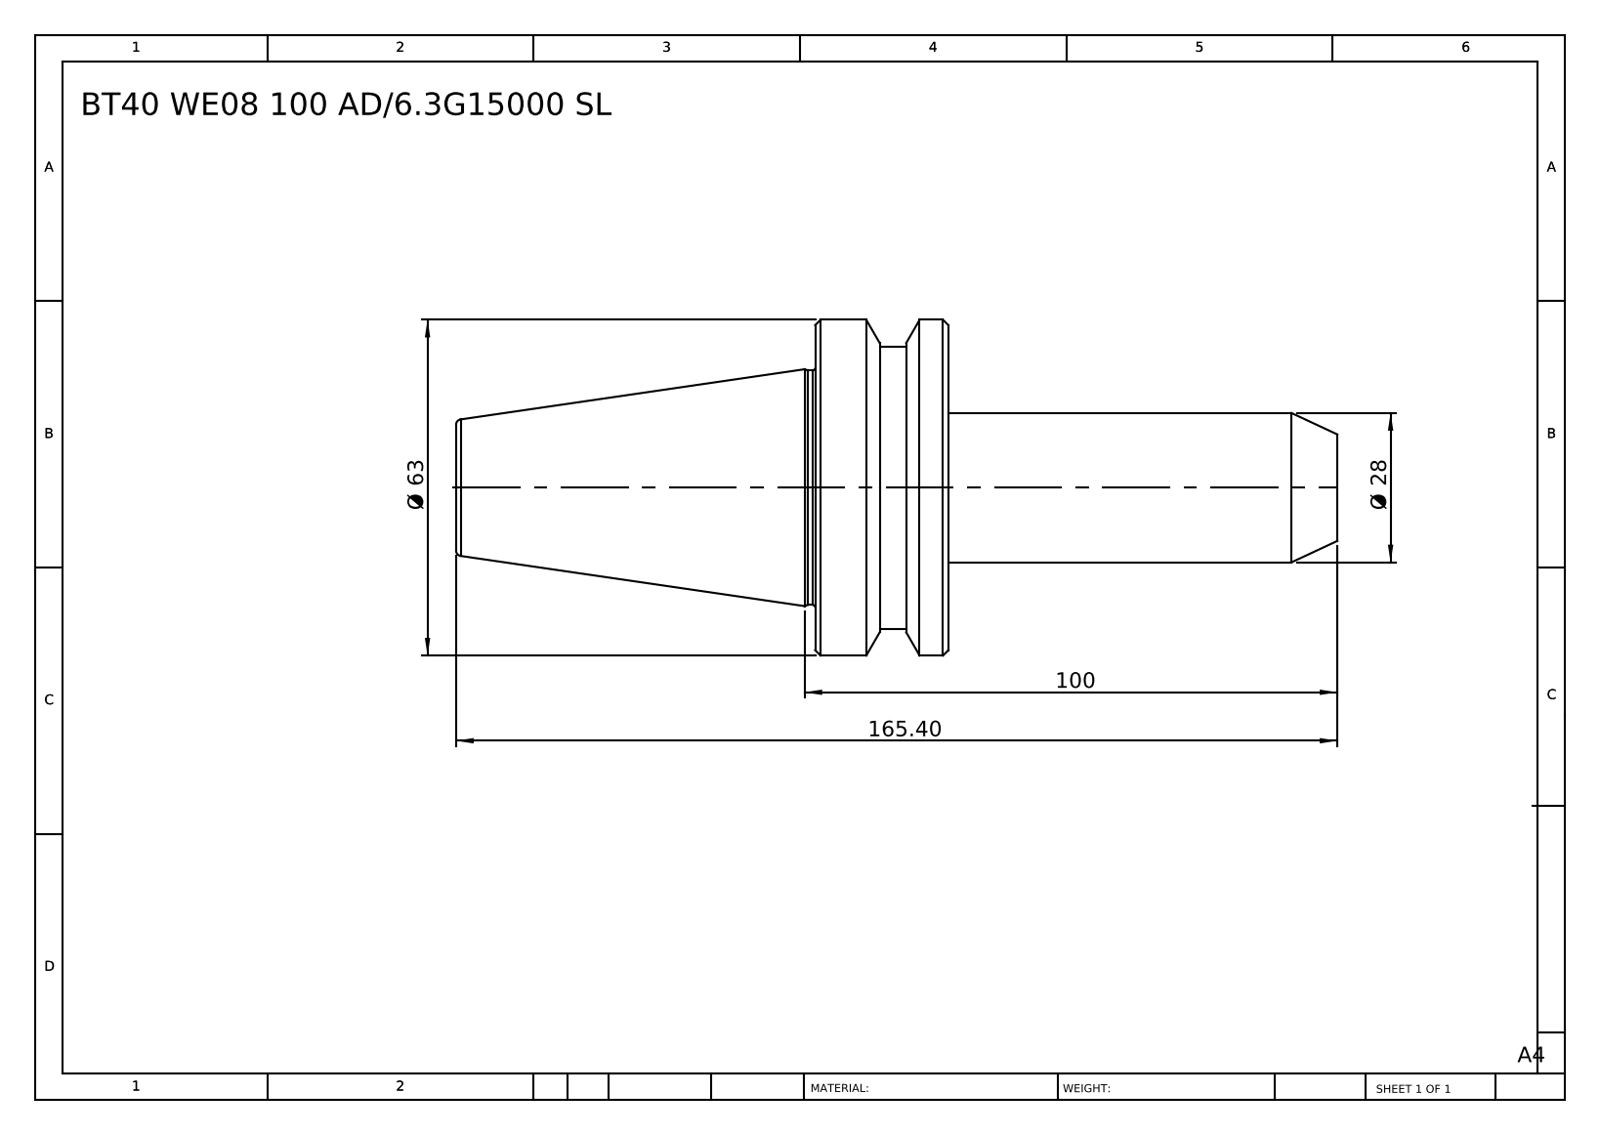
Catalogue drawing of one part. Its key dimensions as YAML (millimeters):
part_name: "BT40 WE08 100 AD-6.3G15000 SL"
step_written_by: "SolidWorks 2014 (CONFIG_CONTROL_DESIGN)"
units: millimeters
bodies: {solids: 1, faces: 36, planar: 6, cylindrical: 10, other: 20}
overall_size: [165.4, 63, 63]
volume: 181931
surface_area: 24412
round_bosses_or_shafts:
  - {diameter: 63, count: 1}
  - {diameter: 53, count: 1}
  - {diameter: 44, count: 1}
  - {diameter: 28, count: 1}
face_to_face_distances: [25, 92.4, 67.4, 73, 98, 165.4, 85.9, 12.9, 12.1, 79.5]
